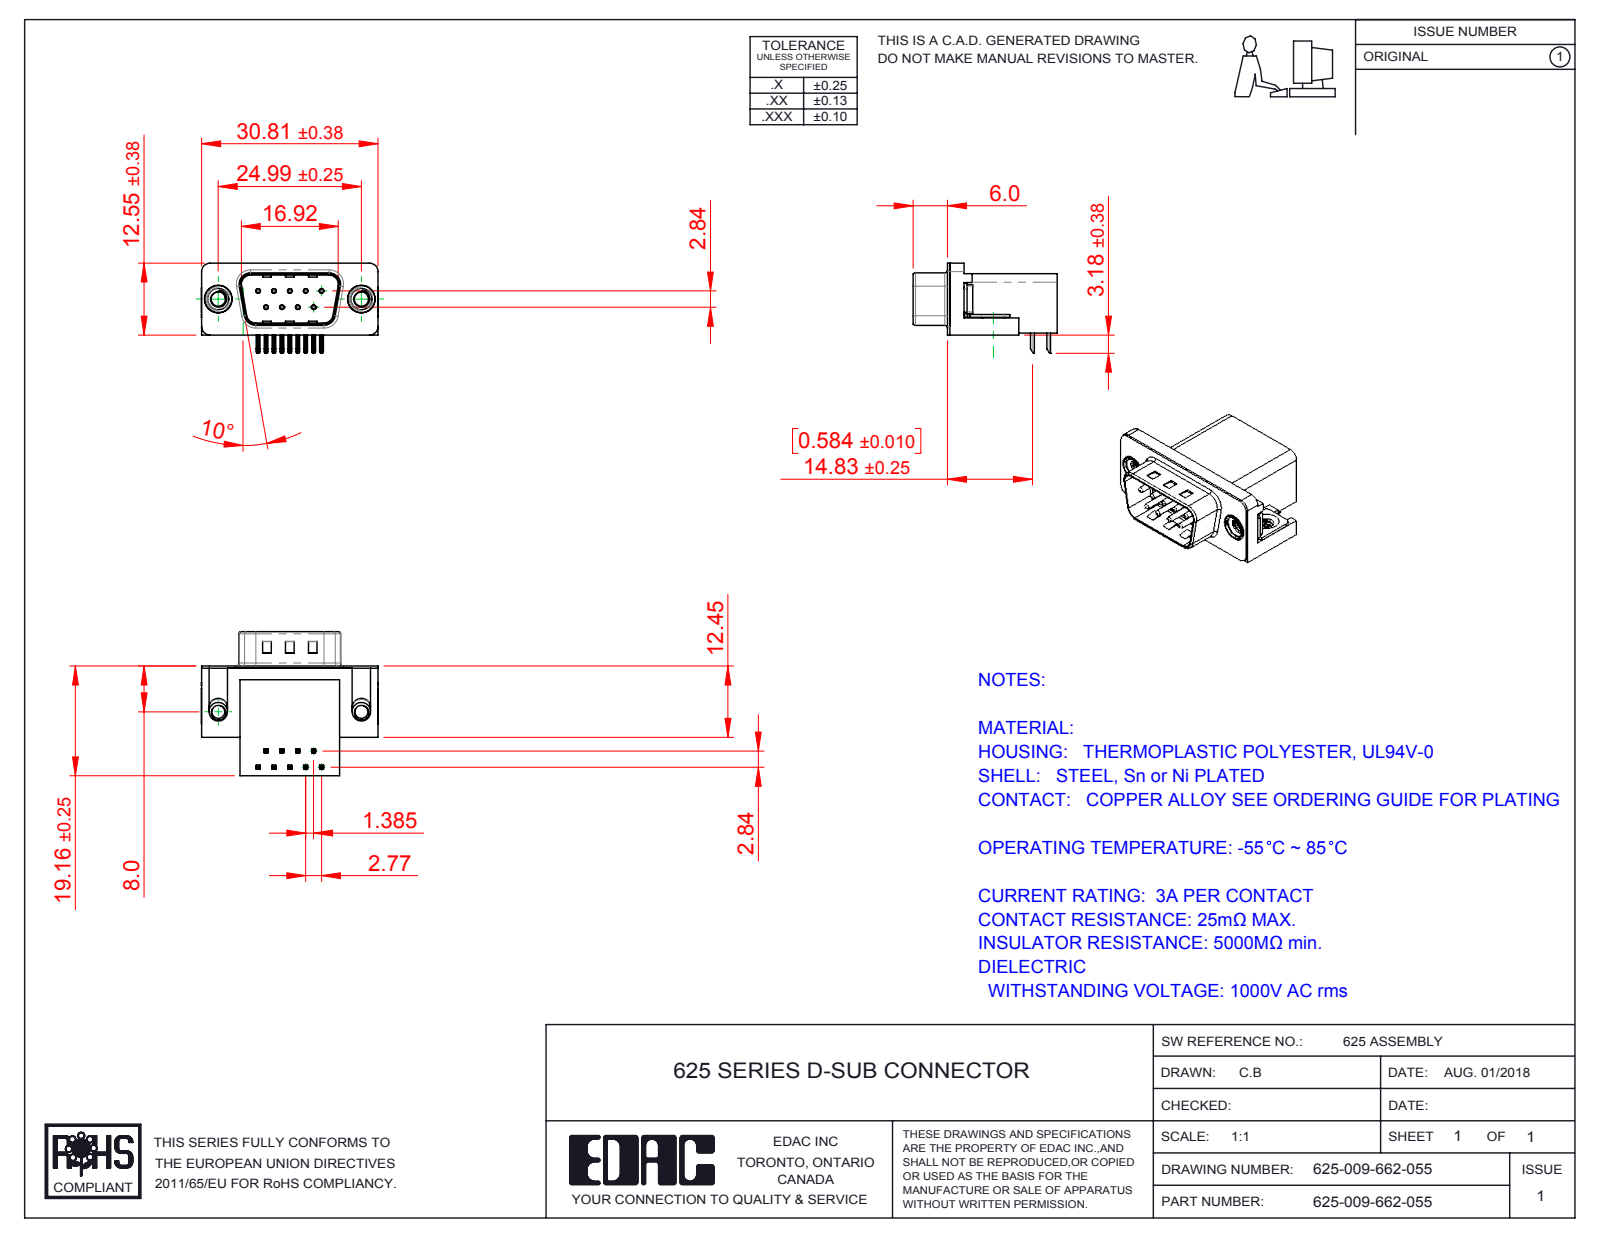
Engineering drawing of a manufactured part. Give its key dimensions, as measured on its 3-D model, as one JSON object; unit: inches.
{"part_name": "625 Shell_9 Socket; 625 4-40 Threaded Board Mount; 625 Contact Bottom; 625 M3 Threaded Rivet (+3 more)", "step_written_by": "SolidWorks 2016 (CONFIG_CONTROL_DESIGN)", "units": "inches", "bodies": {"solids": 15, "faces": 1025, "planar": 575, "cylindrical": 333, "other": 117}, "overall_size": [1.216, 0.991, 0.619], "volume_in3": 0.273, "surface_area_in2": 7.803, "round_holes": [[0.014, 9], [0.031, 9], [0.089, 2], [0.098, 2], [0.157, 2], [0.189, 2], [0.197, 2]], "round_bosses_or_shafts": [[0.03, 9], [0.193, 2], [0.187, 2], [0.154, 2], [0.128, 2]], "partial_cylinders_radius": [[0.01, 44], [0.005, 18], [0.039, 16], [0.02, 9], [0.059, 8], [0.063, 8], [0.035, 4], [0.079, 4]], "face_to_face_distances": [0.016, 0.407, 0.739, 0.754, 0.114, 0.64, 0.098, 0.014, 0.421, 0.264], "hole_center_spacings": [0.124, 0.109, 0.218, 0.198, 0.198, 0.327, 0.294, 0.295]}
